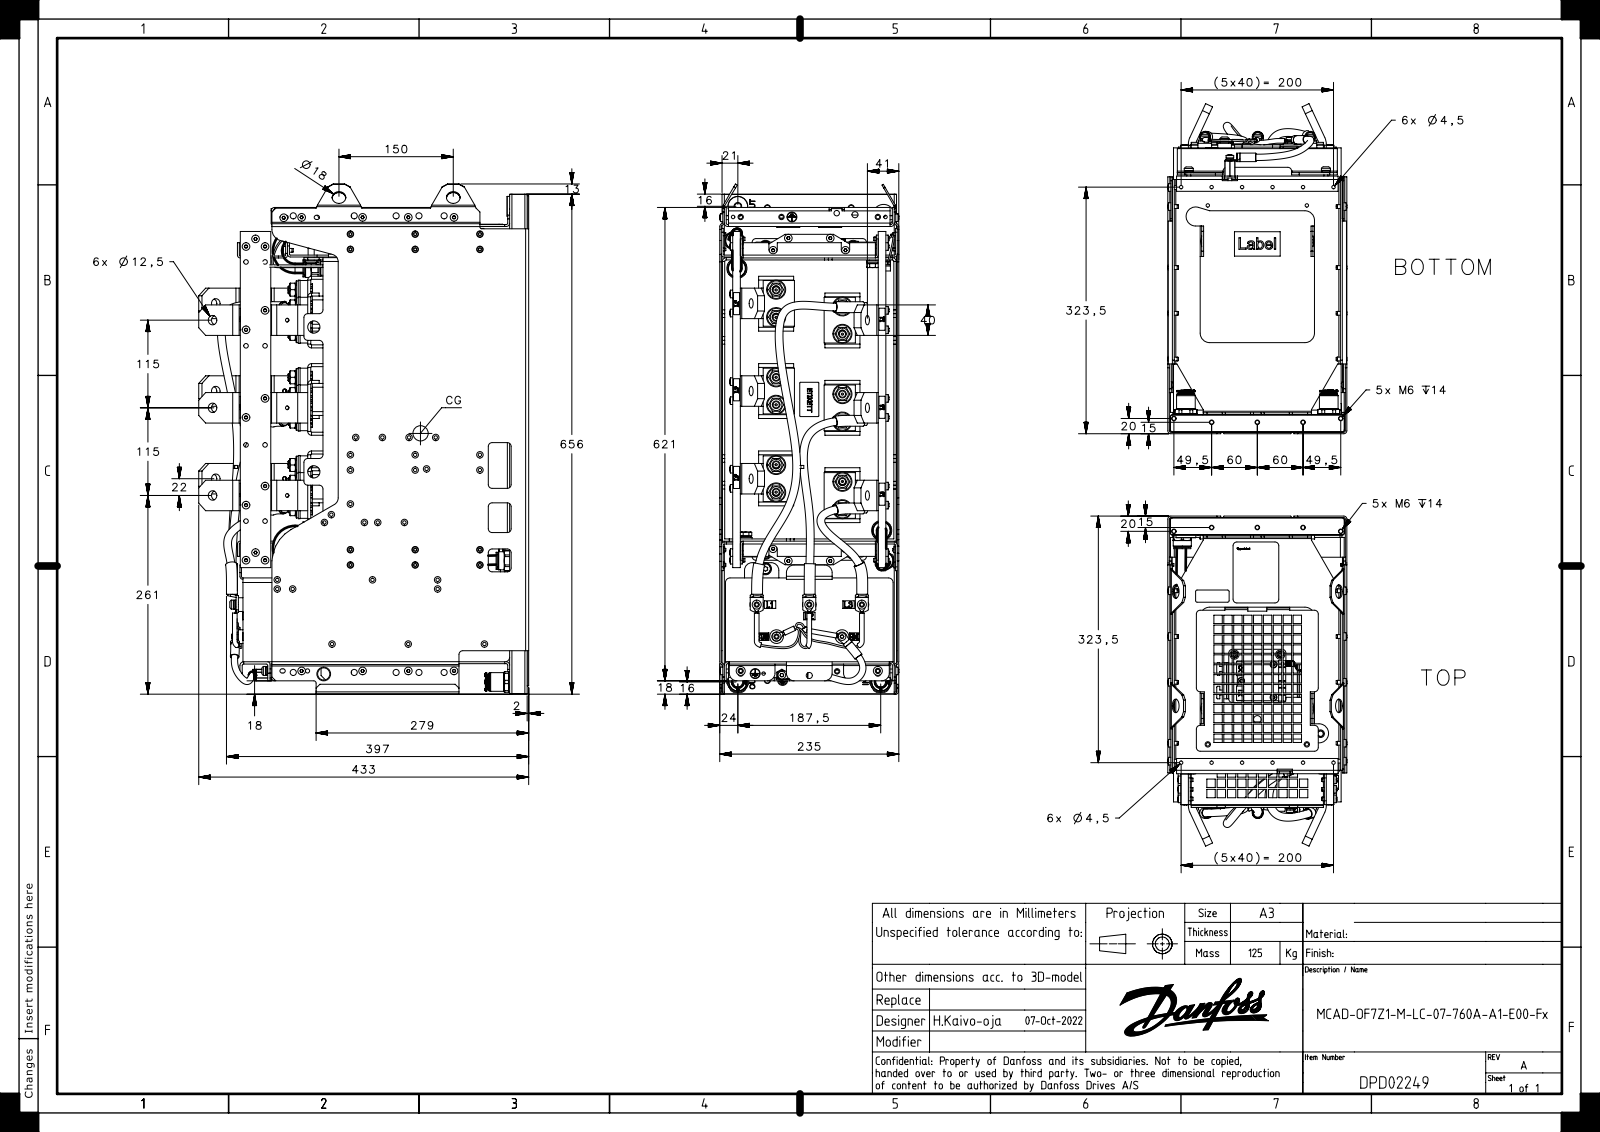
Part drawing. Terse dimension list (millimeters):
written by: SIEMENS PLM Software NX 1892 (AP203_CONFIGURATION_CONTROLLED_3D_DESIGN_OF_MECHANICAL_PARTS_AND_ASSEMBLIES_MIM_LF)
unit: mm
bodies: 304 solids, 10733 faces (6206 planar, 2884 cylindrical, 1643 other)
size: 669.31 × 433.04 × 235
volume: 35 820 000 mm³; area: 3 202 000 mm²
holes: 37× ⌀4.5, 37× ⌀6, 32× ⌀5, 16× ⌀4.6, 15× ⌀8, 15× ⌀8.5, 12× ⌀10.5, 12× ⌀15, 9× ⌀5.5, 9× ⌀9, 8× ⌀7.2, 8× ⌀11
bosses: 56× ⌀10, 47× ⌀5, 30× ⌀8, 27× ⌀4, 15× ⌀1, 12× ⌀25, 12× ⌀7.5, 11× ⌀6.5
rounds: 324× R0.42, 324× R0.88, 106× R5, 54× R0.47, 54× R0.53, 54× R1.08, 54× R1.6, 35× R2
face distances: 2, 233, 2.5, 1.5, 3.5, 25, 231.5, 229.5, 231, 4
hole spacings: 115, 25, 230, 12.5, 16.01, 411.69, 10, 69
